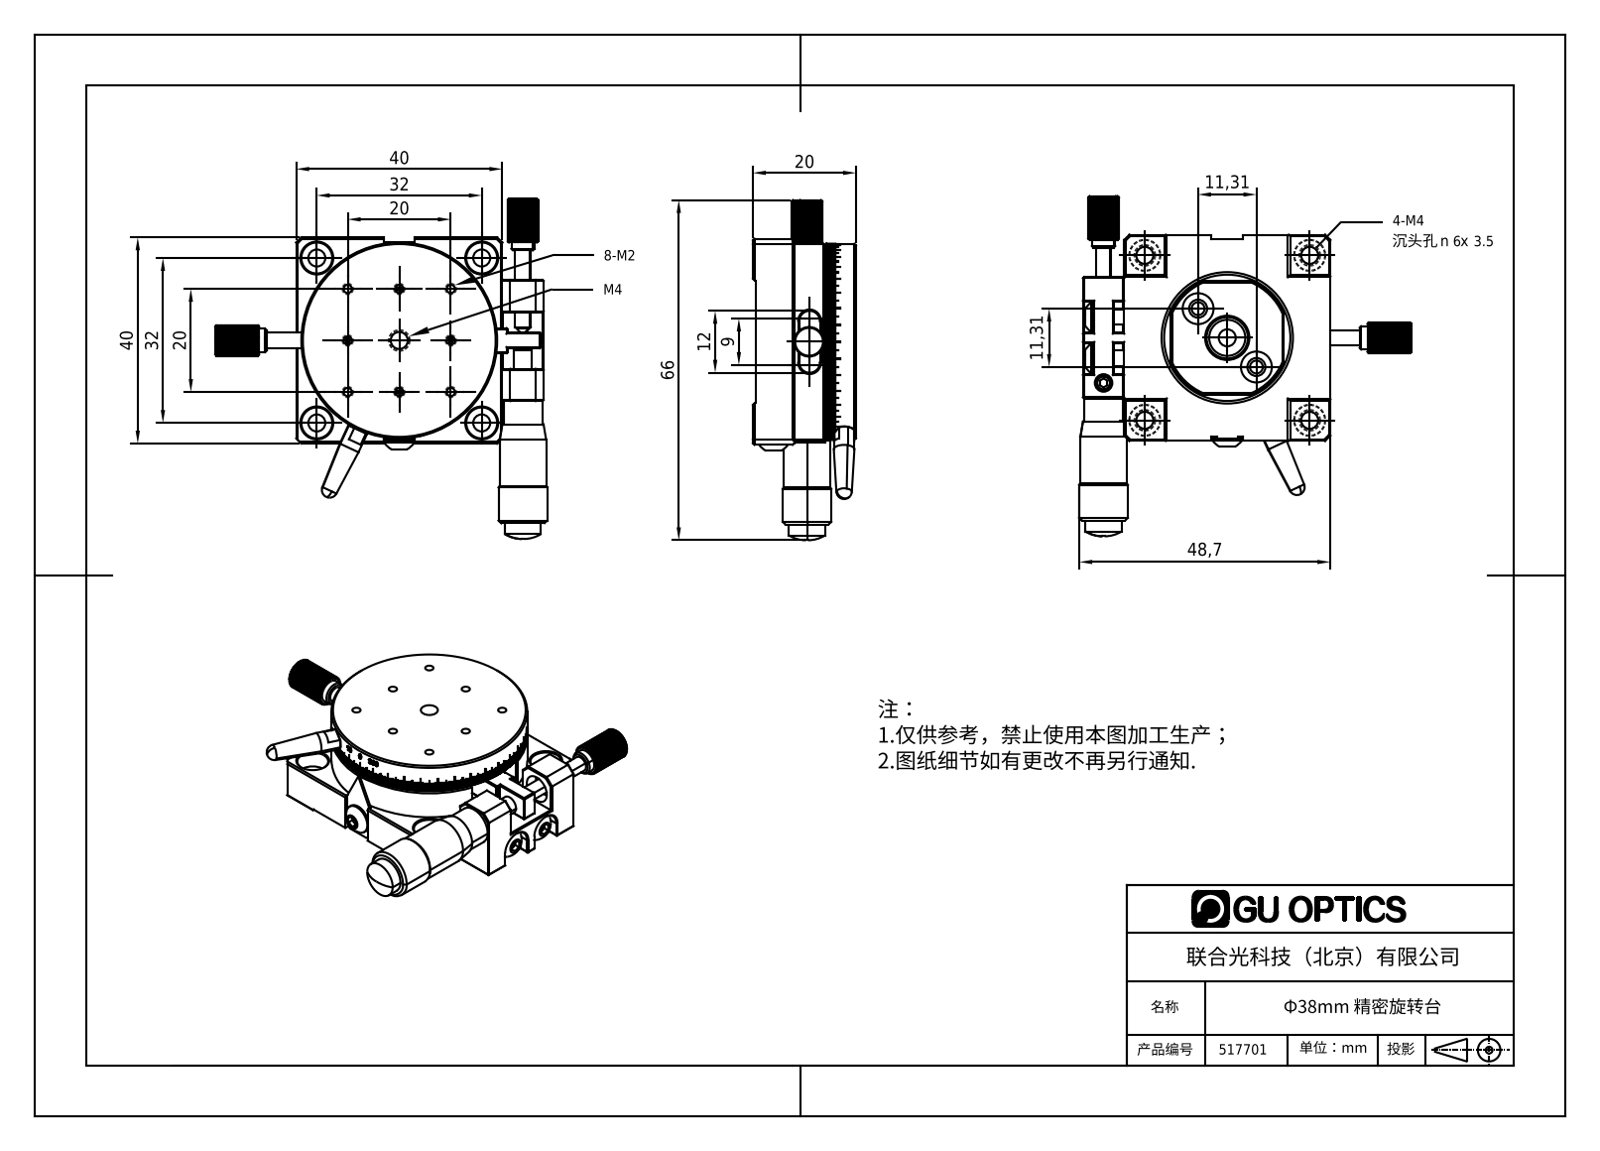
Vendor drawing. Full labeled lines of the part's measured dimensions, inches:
Part name (STEP PRODUCT): SEMR38-AR
STEP written by: SolidWorks 2020 (CONFIG_CONTROL_DESIGN)
Units: inches
Bodies: 5 solids, 2376 faces (1641 planar, 536 cylindrical, 199 other)
Overall size (bounding box): 2.598 × 2.535 × 0.787
Volume: 1.644 in³ · Surface area: 22.26 in²
Round holes (diameter × count): ⌀0.063 ×8, ⌀0.236 ×7, ⌀0.102 ×6, ⌀0.098 ×5, ⌀0.13 ×5, ⌀0.138 ×5, ⌀0.065 ×2, ⌀0.217 ×1, ⌀0.276 ×1, ⌀0.315 ×1, ⌀0.791 ×1, ⌀0.866 ×1
Round bosses / shafts (diameter × count): ⌀0.118 ×7, ⌀0.224 ×3, ⌀0.177 ×2, ⌀1.496 ×1, ⌀0.787 ×1, ⌀0.37 ×1, ⌀0.354 ×1, ⌀0.295 ×1
Partial cylindrical surfaces — rounded edges, fillets, slot ends (radius × count): R0.039 ×2, R0.079 ×2, R0.118 ×2, R0.382 ×1, R0.472 ×1, R0.744 ×1
Main face-to-face distances: 0.236, 0.768, 0.295, 0.531, 0.472, 1.575, 0.315, 0.551, 0.244, 0.02
Hole centre spacings: 0.394, 0.557, 0.673, 0.88, 1.05, 1.202, 0.787, 0.281
